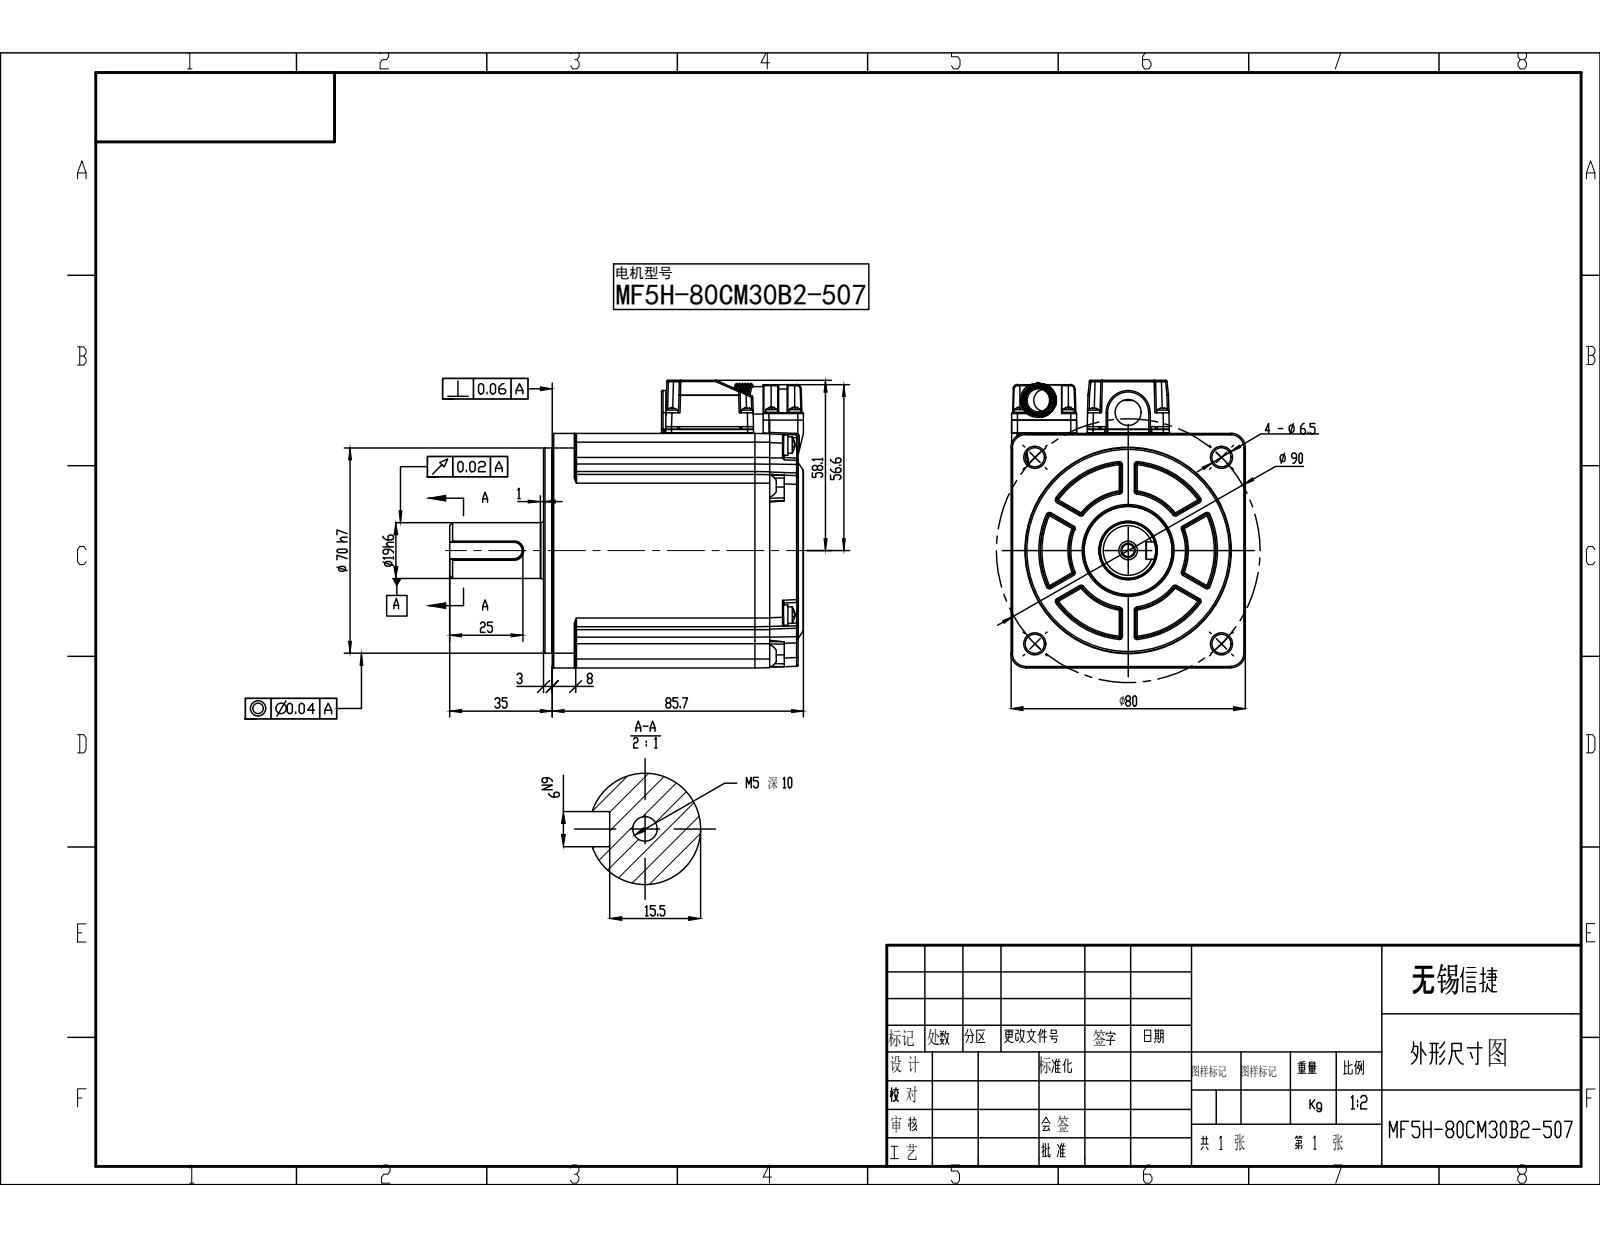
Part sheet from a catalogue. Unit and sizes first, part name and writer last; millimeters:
Units: millimetres
Overall size (bounding box): 120.7 × 98.1 × 80
Round holes (diameter × count): ⌀6.5 ×4, ⌀4.2 ×1, ⌀8.8 ×1, ⌀20 ×1
Round bosses / shafts (diameter × count): ⌀4 ×8, ⌀7 ×4, ⌀5.6 ×4, ⌀70 ×1, ⌀30 ×1, ⌀19.8 ×1, ⌀19 ×1, ⌀11.46 ×1
Partial cylindrical surfaces — rounded edges, fillets, slot ends (radius × count): R0.5 ×66, R0.3 ×41, R3 ×29, R0.2 ×24, R0.35 ×24, R2 ×16, R1 ×9, R0.25 ×4
Main face-to-face distances: 80, 14, 66, 9.7, 1.8, 74.2, 11.5, 85.7, 83.9, 3
Hole centre spacings: 45, 63.64, 35.3, 85.09, 90, 47.1
Bodies: 0 solids, 1181 faces (416 planar, 359 cylindrical, 406 other)
Part name (STEP PRODUCT): MF5H-80CM30B2-507
STEP written by: SolidWorks 2022 (CONFIG_CONTROL_DESIGN)
